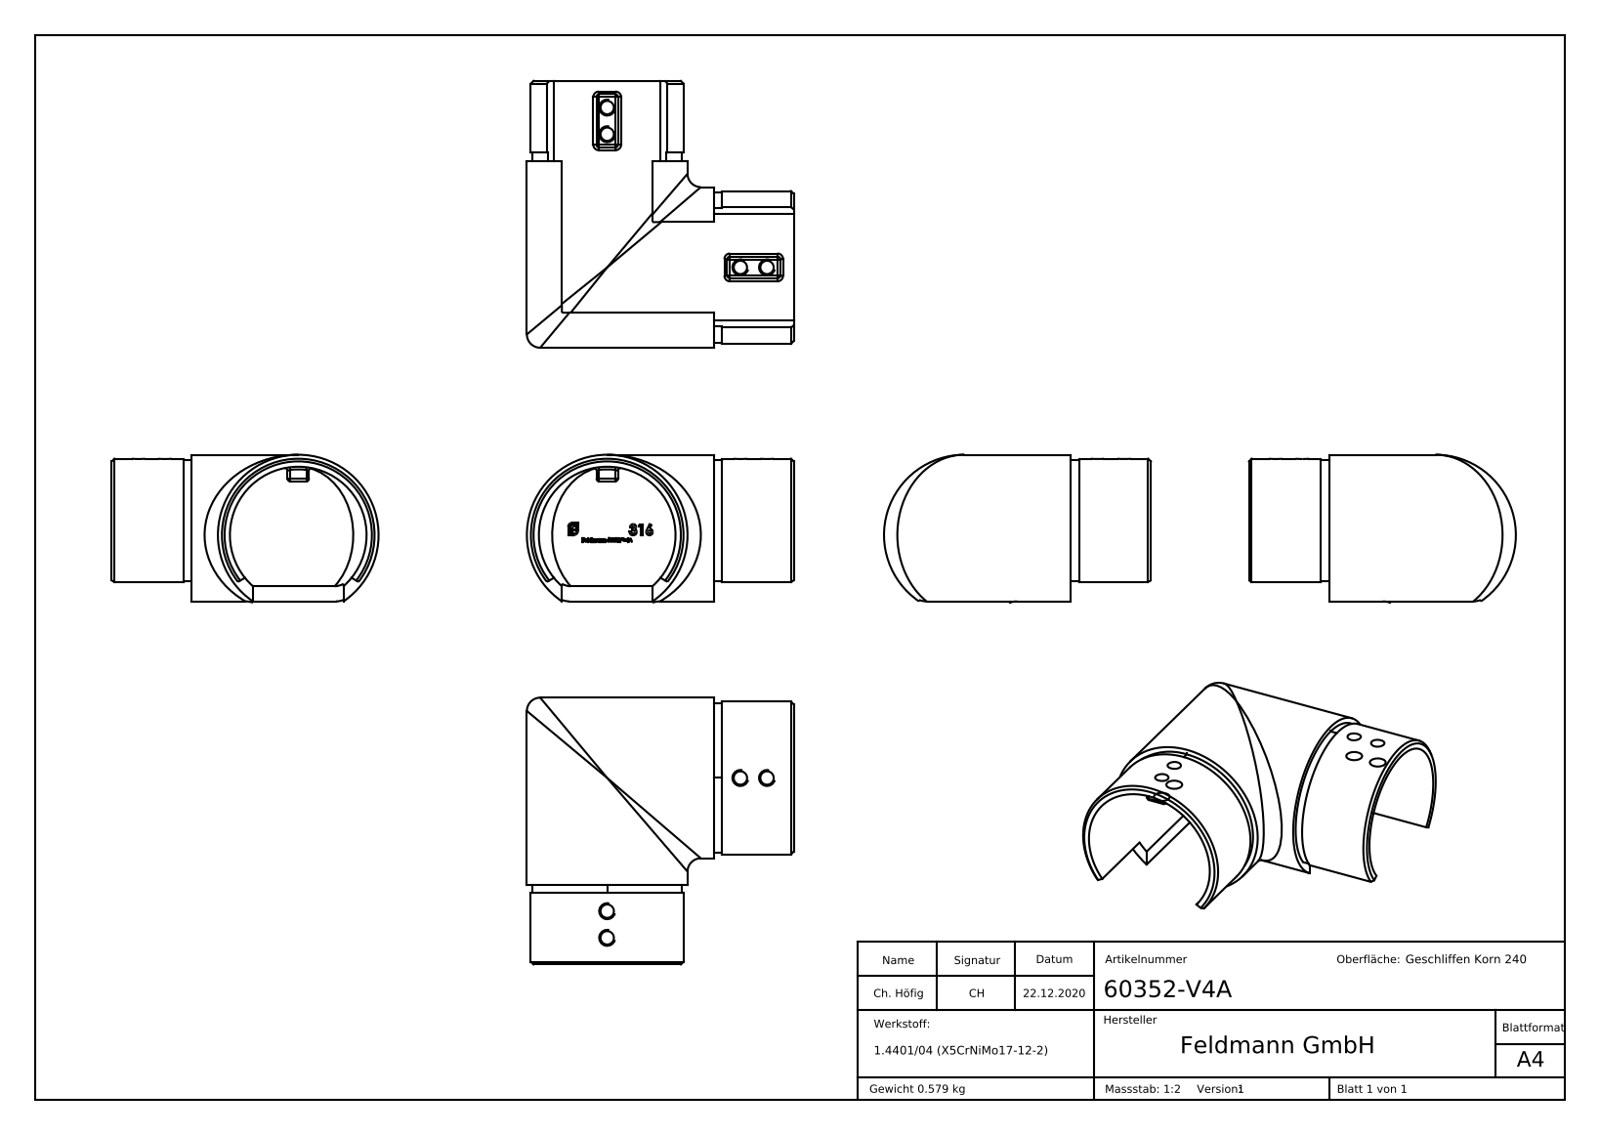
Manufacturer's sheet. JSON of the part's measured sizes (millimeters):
{"part_name": "60352-V4A", "step_written_by": "SolidWorks 2018 (CONFIG_CONTROL_DESIGN)", "units": "millimeters", "bodies": {"solids": 1, "faces": 414, "planar": 165, "cylindrical": 84, "other": 165}, "overall_size": [100.15, 100.15, 55.51], "volume_mm3": 72371, "surface_area_mm2": 39934, "round_holes": [[5, 4]], "round_bosses_or_shafts": [[60.3, 2]], "partial_cylinders_radius": [[1, 20], [25.65, 2], [28.15, 2], [28.65, 2], [25.75, 1]], "face_to_face_distances": [57, 87, 30, 34, 23, 53, 13, 21, 60, 26], "hole_center_spacings": [10, 78.1, 70.71, 84.85]}
